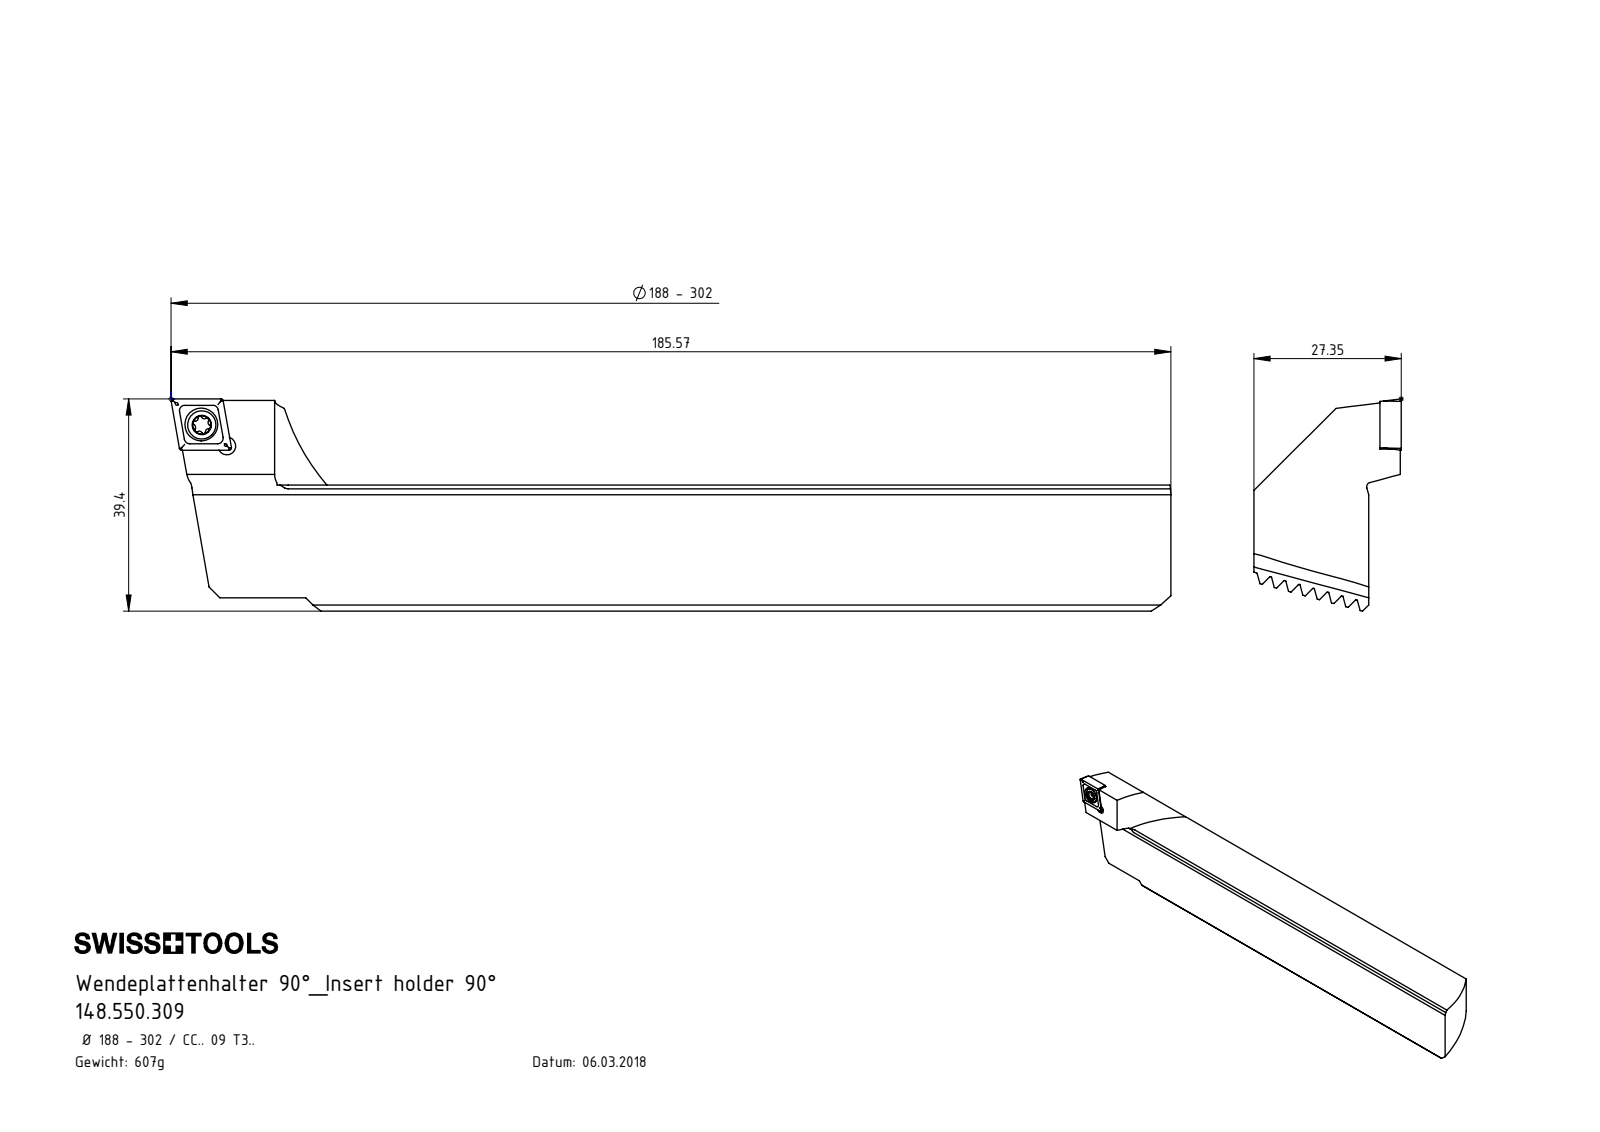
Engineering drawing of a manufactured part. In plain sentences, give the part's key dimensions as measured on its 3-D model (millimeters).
The part is named "F00-WCB.188.001_C; WCB-ER2.001.009_A; CCMT09T304; 148.550.309". Its 3-D file was written by "SolidWorks 2017 (CONFIG_CONTROL_DESIGN)". It is 3 solids with 694 faces: 422 planar, 39 cylindrical and 233 other. Overall it measures 185.57 by 39.4 by 27.35 millimeters. Its volume is 77 331 cubic millimeters and its surface area 18 926 square millimeters. Round holes: 2 of diameter 3.3, 1 of diameter 4.4, 1 of diameter 6.1. Round bosses or shafts: 1 of diameter 5.25, 1 of diameter 4. Partial cylindrical surfaces (rounded edges, fillets, slot ends): 8 of radius 0.2, 6 of radius 0.34, 6 of radius 0.59, 3 of radius 40, 1 of radius 0.8. The main face-to-face distances are 2.38, 21.3, 4.76, 7.14, 9.52, 4.77, 7.15, 9.53, 11.91, 14.29. The hole center spacings are 6.06, 6.19.
